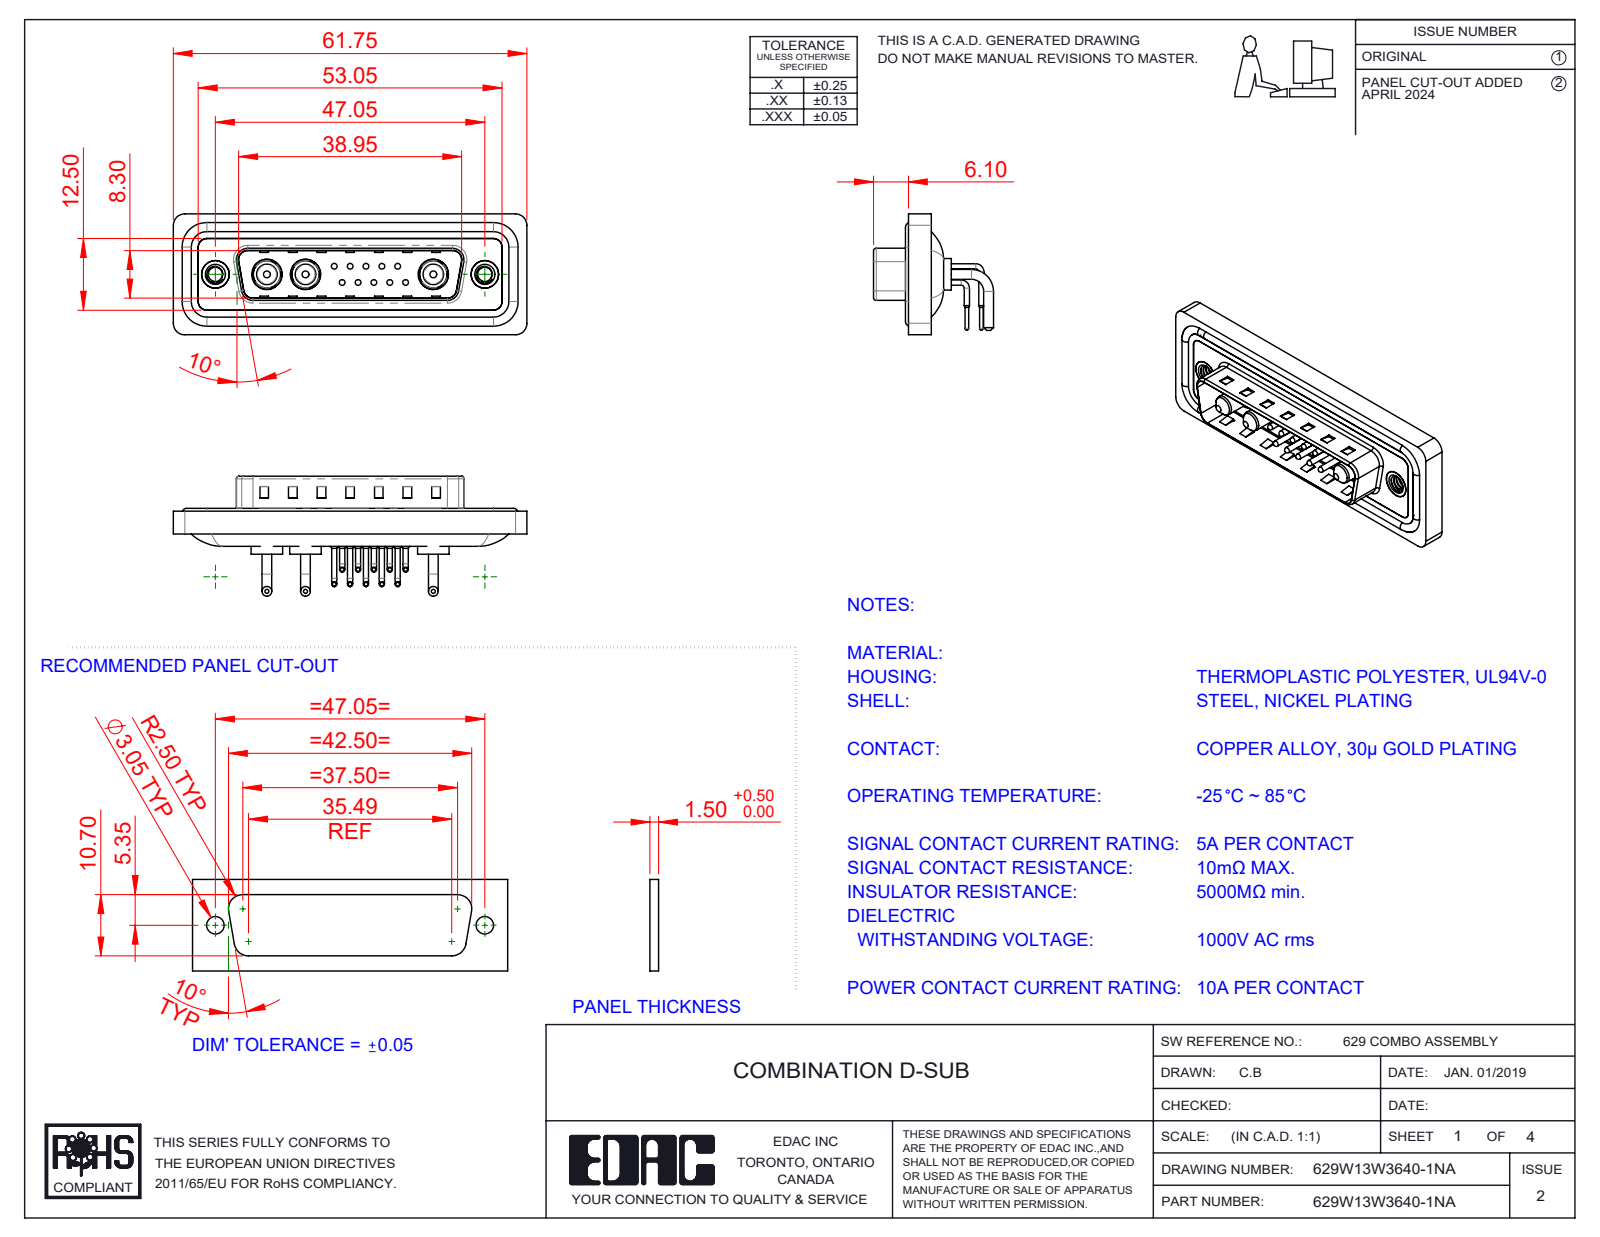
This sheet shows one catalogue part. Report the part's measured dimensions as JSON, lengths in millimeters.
{"part_name": "629Combo Threaded Rivet_A; 629Combo Shell Rear_25 Contacts; 629Combo Waterproof Housing_25 Contacts; 629Combo Contact Row 1 (+5 more)", "step_written_by": "SolidWorks 2023 (CONFIG_CONTROL_DESIGN)", "units": "millimeters", "bodies": {"solids": 23, "faces": 1706, "planar": 879, "cylindrical": 609, "other": 218}, "overall_size": [61.75, 21.1, 20.95], "volume_mm3": 7440, "surface_area_mm2": 12347, "round_holes": [[0.75, 10], [1.6, 10], [2, 10], [4.85, 3], [5.3, 3], [2.5, 2], [4, 2], [4.8, 2], [5, 2]], "round_bosses_or_shafts": [[0.9, 20], [1.5, 10], [1, 10], [0.65, 10], [1.7, 6], [1.6, 4], [5.5, 3], [5.2, 3]], "partial_cylinders_radius": [[1.5, 18], [2, 18], [1.01, 10], [0.5, 8], [1.6, 8], [0.25, 4], [0.6, 4], [0.65, 4]], "face_to_face_distances": [0.4, 2.9, 0.8, 4.1, 1.1, 2.1, 1.6, 4.5, 1.5, 6], "hole_center_spacings": [3.16, 2.77, 5.04, 5.54, 7.49, 5.03, 8.31, 10.11]}
